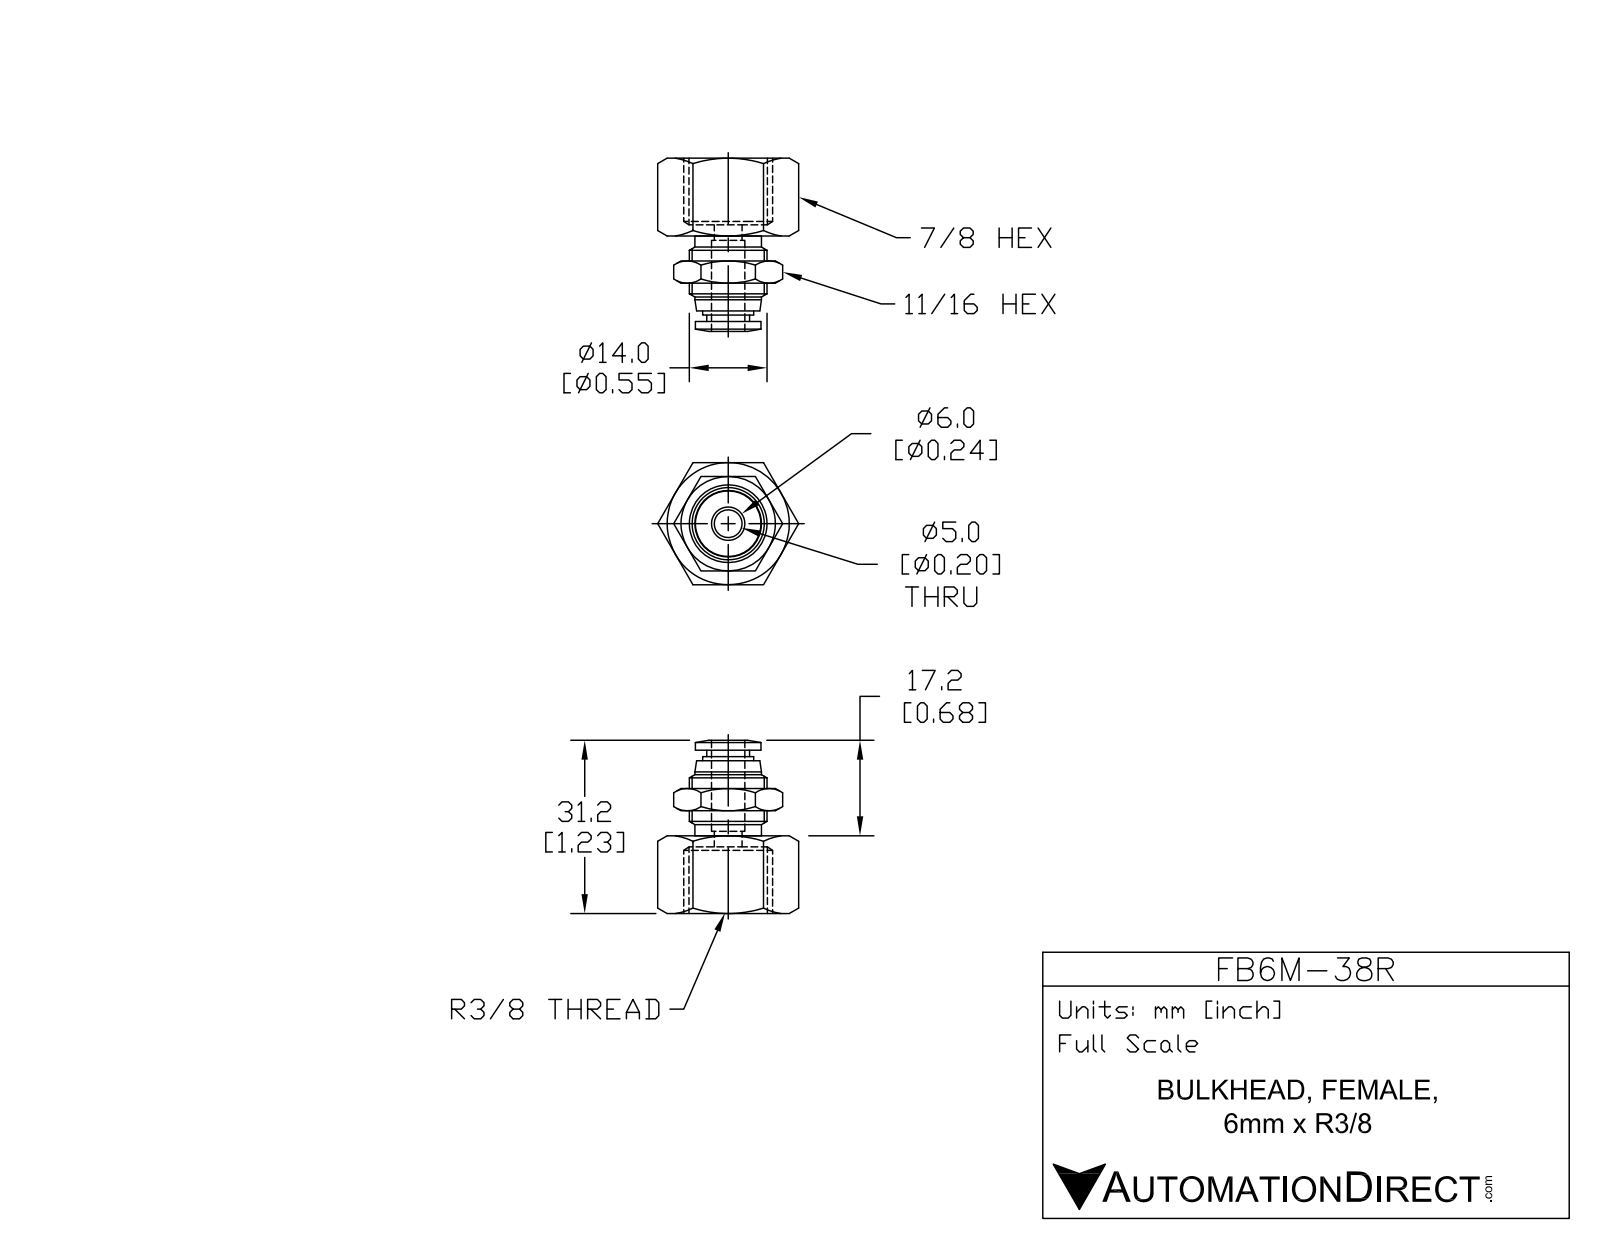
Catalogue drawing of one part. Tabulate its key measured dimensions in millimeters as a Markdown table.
| quantity | value |
| --- | --- |
| part name | FB6M-38R |
| STEP written by | SolidWorks 2015 (AUTOMOTIVE_DESIGN) |
| units | millimeters |
| bodies | 1 solid, 80 faces (22 planar, 18 cylindrical, 40 other) |
| overall size | 31.2 × 25.4 × 22 |
| volume | 5 290 mm³ |
| surface area | 3 842 mm² |
| round holes (diameter × count) | 5 × 1, 6.3 × 1 |
| round bosses / shafts (diameter × count) | 14 × 1, 12 × 1, 11.8 × 1, 9.2 × 1, 7.7 × 1 |
| main face-to-face distances | 22, 19.5, 2.5, 2, 12, 14, 17, 22.3, 10.3, 8.3 |
